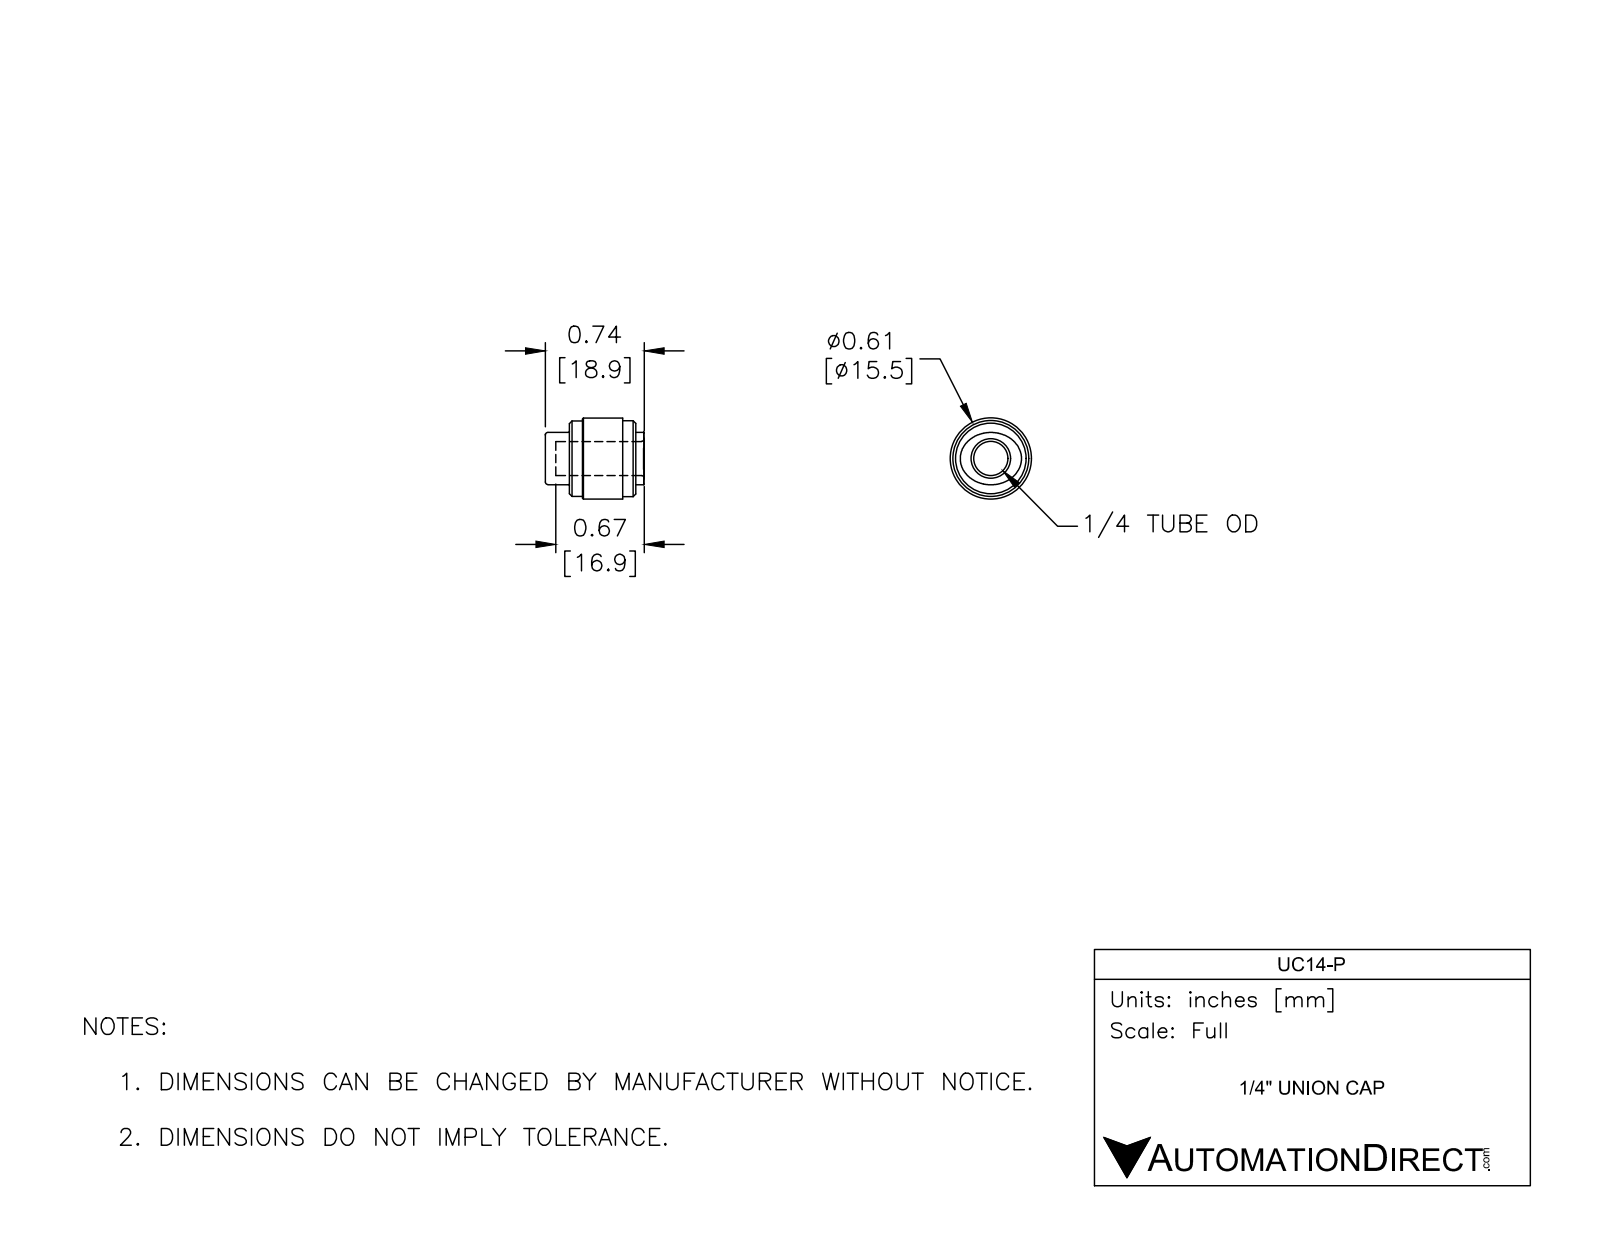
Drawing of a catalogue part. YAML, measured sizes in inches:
part_name: "UC14-P"
step_written_by: "SolidWorks 2017 (AUTOMOTIVE_DESIGN)"
units: inches
bodies: {solids: 1, faces: 38, planar: 7, cylindrical: 10, other: 21}
overall_size: [0.744, 0.61, 0.61]
volume: 0.134
surface_area: 2.285
round_holes:
  - {diameter: 0.256, count: 1}
round_bosses_or_shafts:
  - {diameter: 0.61, count: 1}
  - {diameter: 0.571, count: 1}
  - {diameter: 0.567, count: 1}
  - {diameter: 0.394, count: 1}
face_to_face_distances: [0.181, 0.681, 0.5, 0.098, 0.402, 0.079, 0.102, 0.602, 0.583, 0.504]
